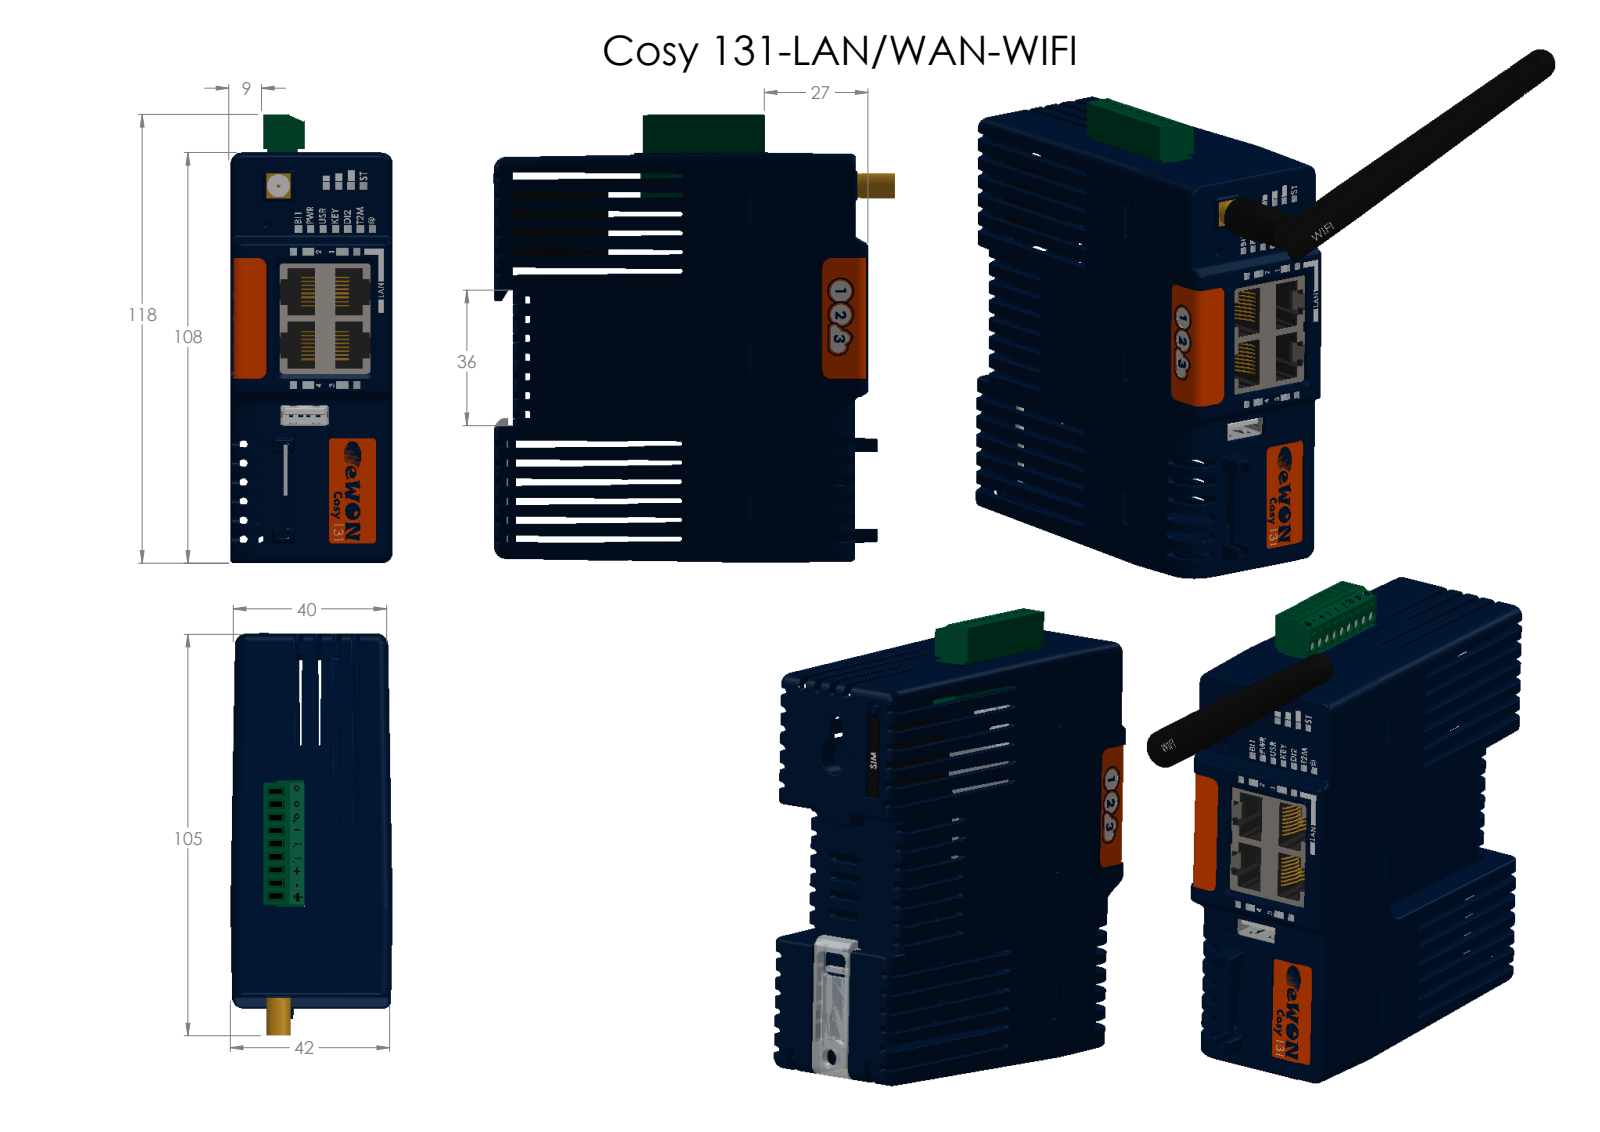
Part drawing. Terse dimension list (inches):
name: DEFAULT-22; DEFAULT-12; DEFAULT-6; DEFAULT-9 (+8 more)
written by: SolidWorks 2015 (AUTOMOTIVE_DESIGN)
unit: in
bodies: 74 solids, 7315 faces (4325 planar, 1724 cylindrical, 1266 other)
size: 6.08 × 5.714 × 3.045
volume: 5.683 in³; area: 203 in²
holes: 17× ⌀0.039, 16× ⌀0.018, 9× ⌀0.031, 9× ⌀0.079, 9× ⌀0.118, 2× ⌀0.236, 1× ⌀0.071, 1× ⌀0.177, 1× ⌀0.209, 1× ⌀0.216, 1× ⌀0.245, 1× ⌀0.248
bosses: 16× ⌀0.018, 9× ⌀0.02, 1× ⌀0.394, 1× ⌀0.374, 1× ⌀0.366, 1× ⌀0.293, 1× ⌀0.282, 1× ⌀0.25
rounds: 293× R0.01, 133× R0.02, 116× R0.008, 80× R0.039, 74× R0.006, 30× R0.03, 24× R0.005, 24× R0.009
face distances: 0.079, 0.197, 1.598, 0.279, 1.599, 0.394, 1.32, 0.128, 4.163, 0.591
hole spacings: 0.138, 0.112, 0.276, 0.1, 0.413, 0.551, 0.2, 0.556
